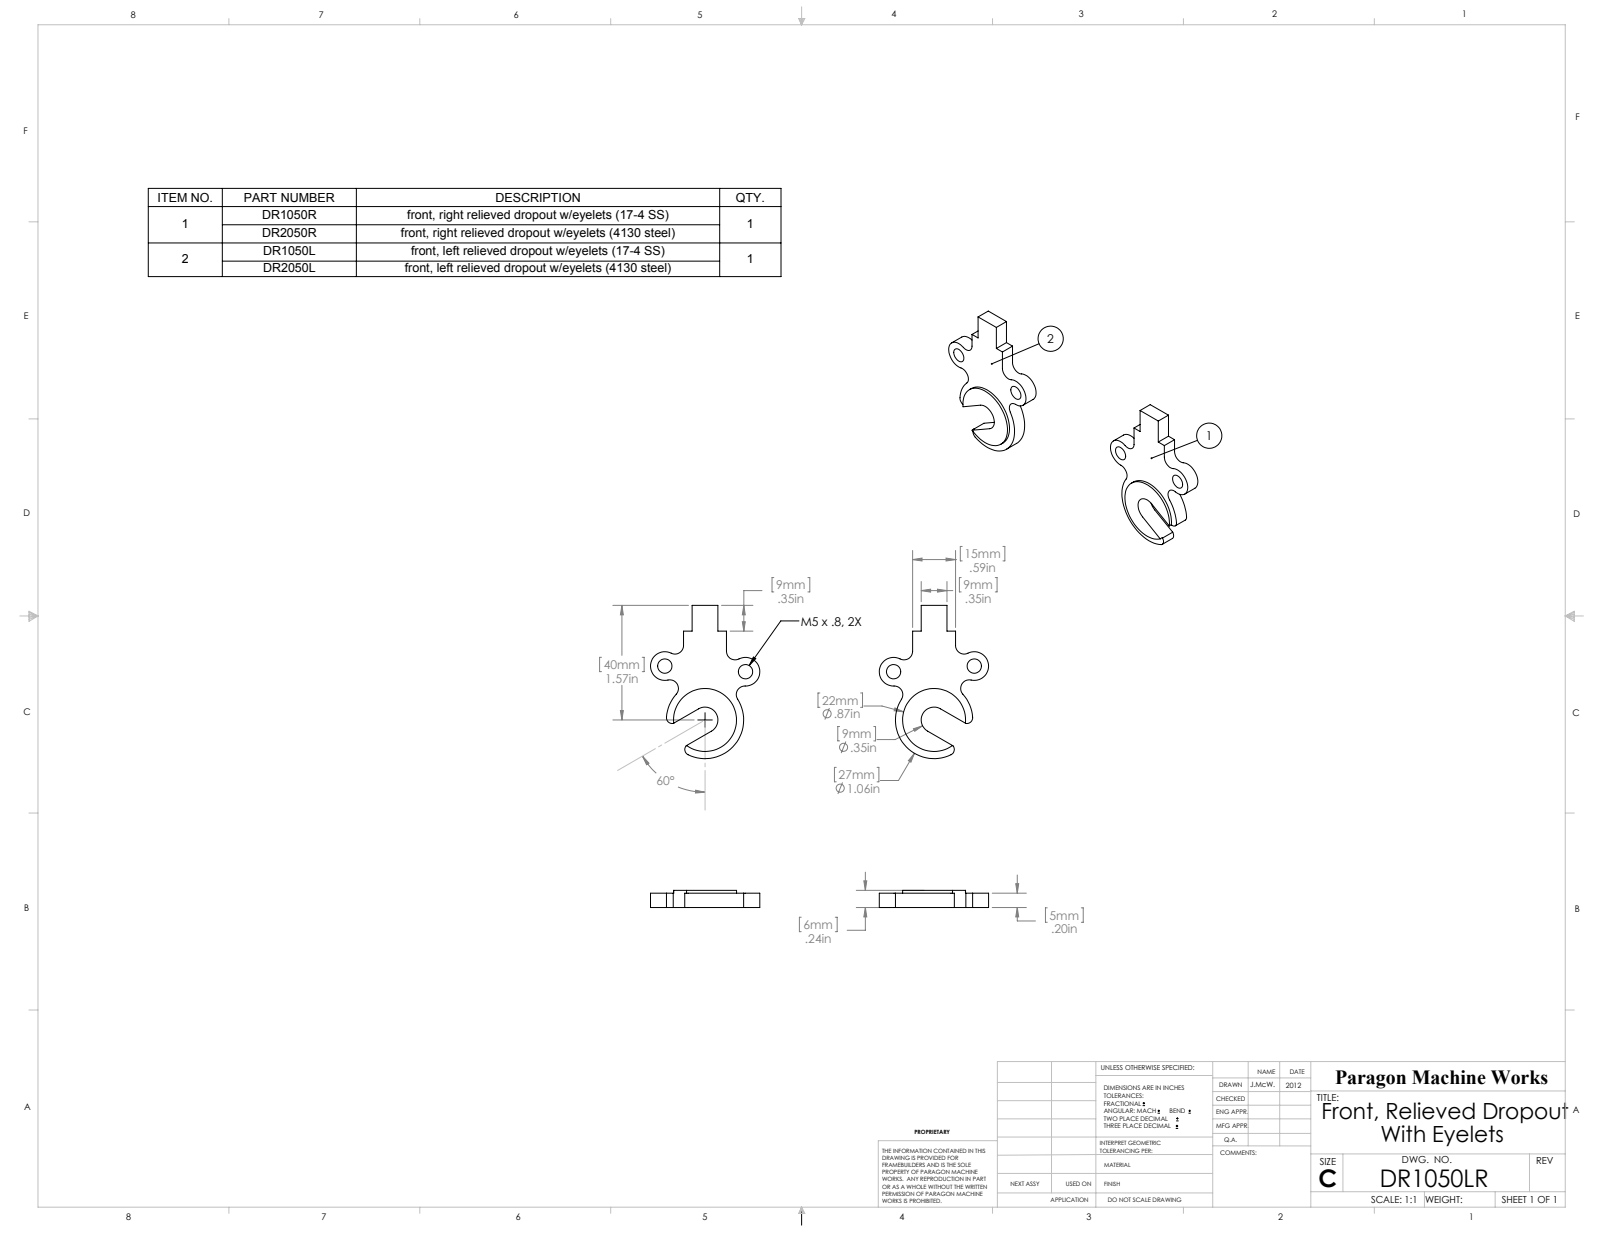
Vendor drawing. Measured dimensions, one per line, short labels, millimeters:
name: DR1050L; DR1050R; DR1050LR
written by: SolidWorks 2012 (AUTOMOTIVE_DESIGN)
unit: mm
bodies: 2 solids, 52 faces (24 planar, 28 cylindrical, 0 other)
size: 118.07 × 53.5 × 6
volume: 10 052 mm³; area: 6 266 mm²
holes: 4× ⌀5
bosses: 2× ⌀22
rounds: 8× R3, 4× R2.03, 4× R5, 2× R4.5, 2× R13.5
face distances: 5, 6, 1, 9, 80, 3, 12, 77, 68, 15
hole spacings: 28.24, 79.91, 51.72, 108.06
